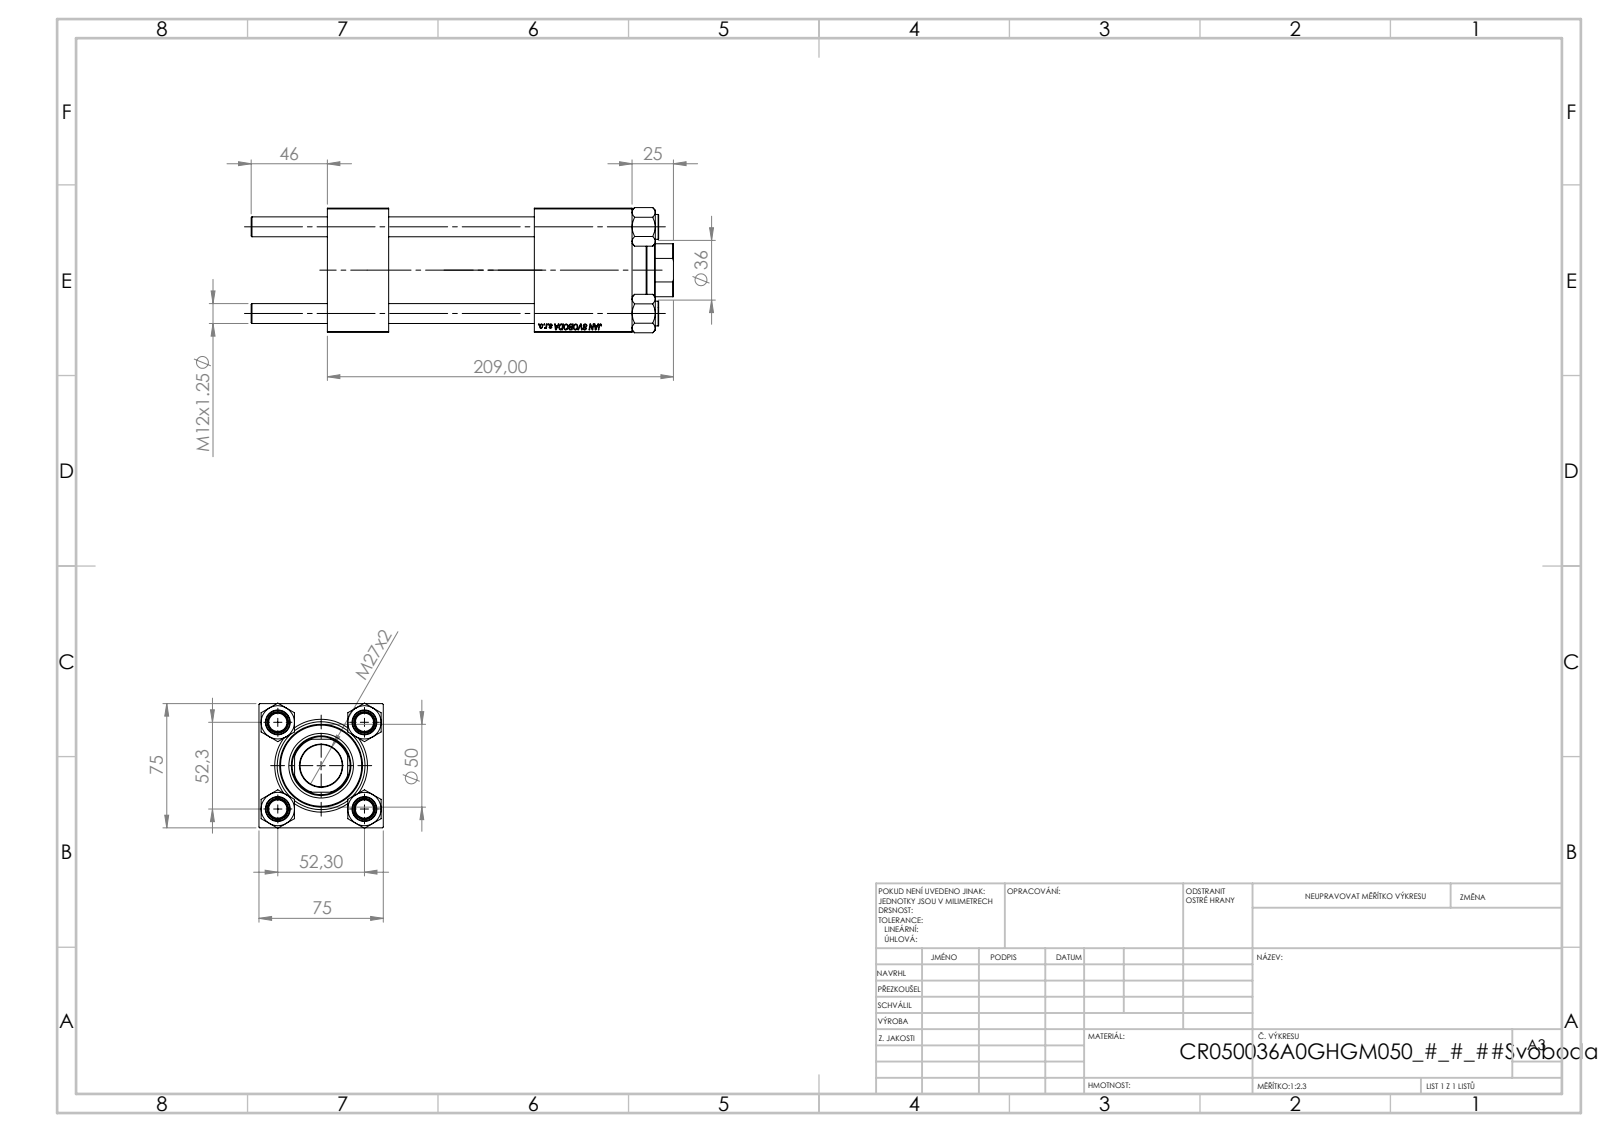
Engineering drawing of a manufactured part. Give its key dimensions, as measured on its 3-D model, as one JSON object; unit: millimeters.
{"part_name": "V215CR_VCP; V215CR_BODY_A; CR025_012_A_0_G_A_G_M_020_+#_##_TYCINKA; V215_VC_A (+1 more)", "step_written_by": "SolidWorks 2019 (CONFIG_CONTROL_DESIGN)", "units": "millimeters", "bodies": {"solids": 11, "faces": 1134, "planar": 520, "cylindrical": 78, "other": 536}, "overall_size": [255, 75.54, 75], "volume_mm3": 778263, "surface_area_mm2": 189854, "round_holes": [[12, 4], [7, 2], [20.96, 2], [30, 2], [25.5, 1], [36, 1], [39, 1], [41, 1], [53, 1]], "round_bosses_or_shafts": [[15, 4], [56, 1], [50, 1]], "partial_cylinders_radius": [[17.5, 1]], "face_to_face_distances": [75, 37, 125, 184, 147, 88, 59, 155.3, 118.3, 30.3], "hole_center_spacings": [36.98, 52.3, 73.96, 123.5]}
